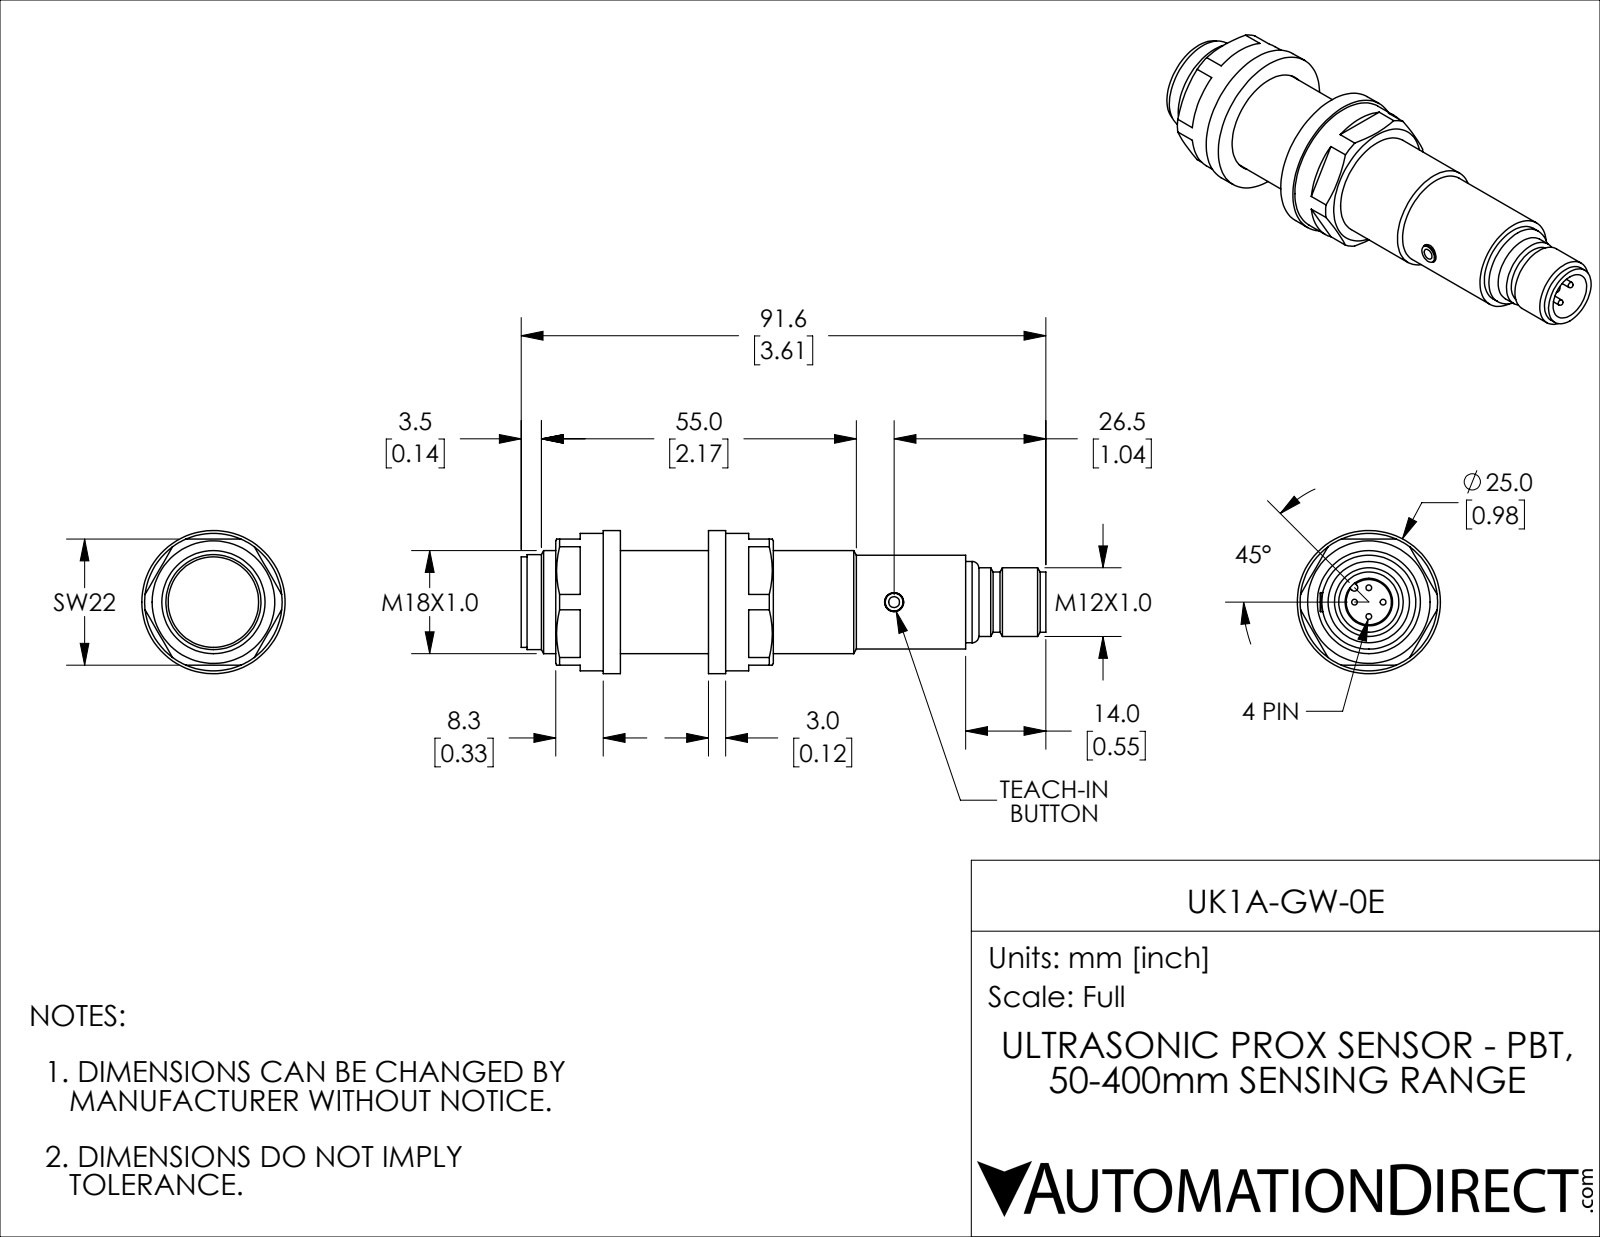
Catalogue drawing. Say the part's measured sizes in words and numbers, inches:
The part is named "UK1A-GW-0E". Its 3-D file was written by "SolidWorks 2018 (AUTOMOTIVE_DESIGN)". It is 6 solids with 123 faces: 43 planar, 49 cylindrical and 31 other. Overall it measures 3.606 by 0.984 by 0.984 inches. Its volume is 1.477 cubic inches and its surface area 16.01 square inches. Round holes: 1 of diameter 0.13, 1 of diameter 0.327, 1 of diameter 0.709, 1 of diameter 0.717. Round bosses or shafts: 4 of diameter 0.039, 1 of diameter 0.984, 1 of diameter 0.945, 1 of diameter 0.654, 1 of diameter 0.646, 1 of diameter 0.622, 1 of diameter 0.559, 1 of diameter 0.472. Partial cylindrical surfaces (rounded edges, fillets, slot ends): 1 of radius 0.024. The main face-to-face distances are 0.118, 0.724, 0.843, 0.606, 0.866, 0.327, 0.445, 1.051, 1.169, 0.563.
